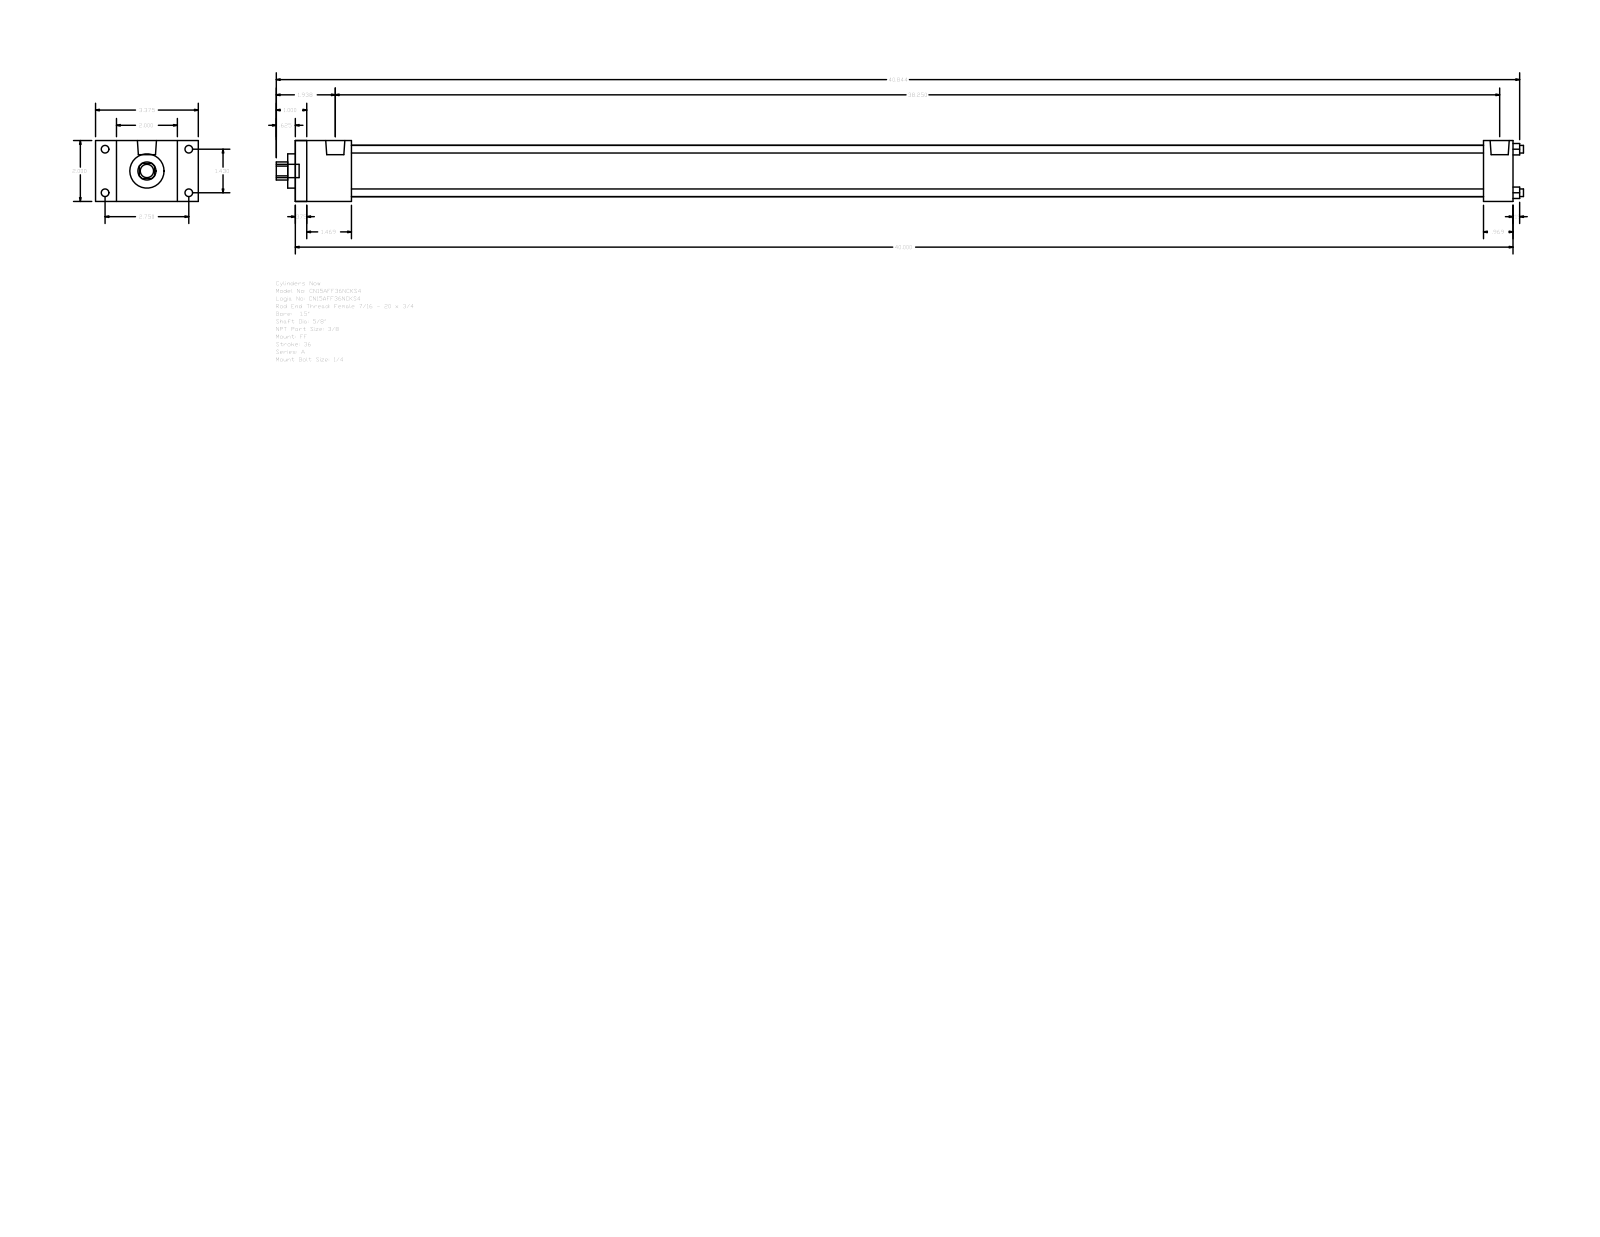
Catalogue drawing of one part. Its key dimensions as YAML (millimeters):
part_name: "A_FF__0150_0.625"
step_written_by: "GSSL Pune (CONFIG_CONTROL_DESIGN)"
units: millimeters
bodies: {solids: 0, faces: 92, planar: 64, cylindrical: 28, other: 0}
overall_size: [1040.61, 85.72, 50.8]
round_holes:
  - {diameter: 6.35, count: 4}
  - {diameter: 15.88, count: 1}
  - {diameter: 28.57, count: 1}
  - {diameter: 42.93, count: 1}
round_bosses_or_shafts:
  - {diameter: 6.35, count: 4}
  - {diameter: 5.56, count: 4}
  - {diameter: 15.93, count: 2}
  - {diameter: 11.11, count: 1}
partial_cylinders:
  - {radius: 7.54, count: 1}
face_to_face_distances: [50.8, 1016, 9.52, 1006.48, 46.83, 991.39, 37.31, 981.87, 944.56, 969.17]
hole_center_spacings: [25.68, 36.32, 51.36]
